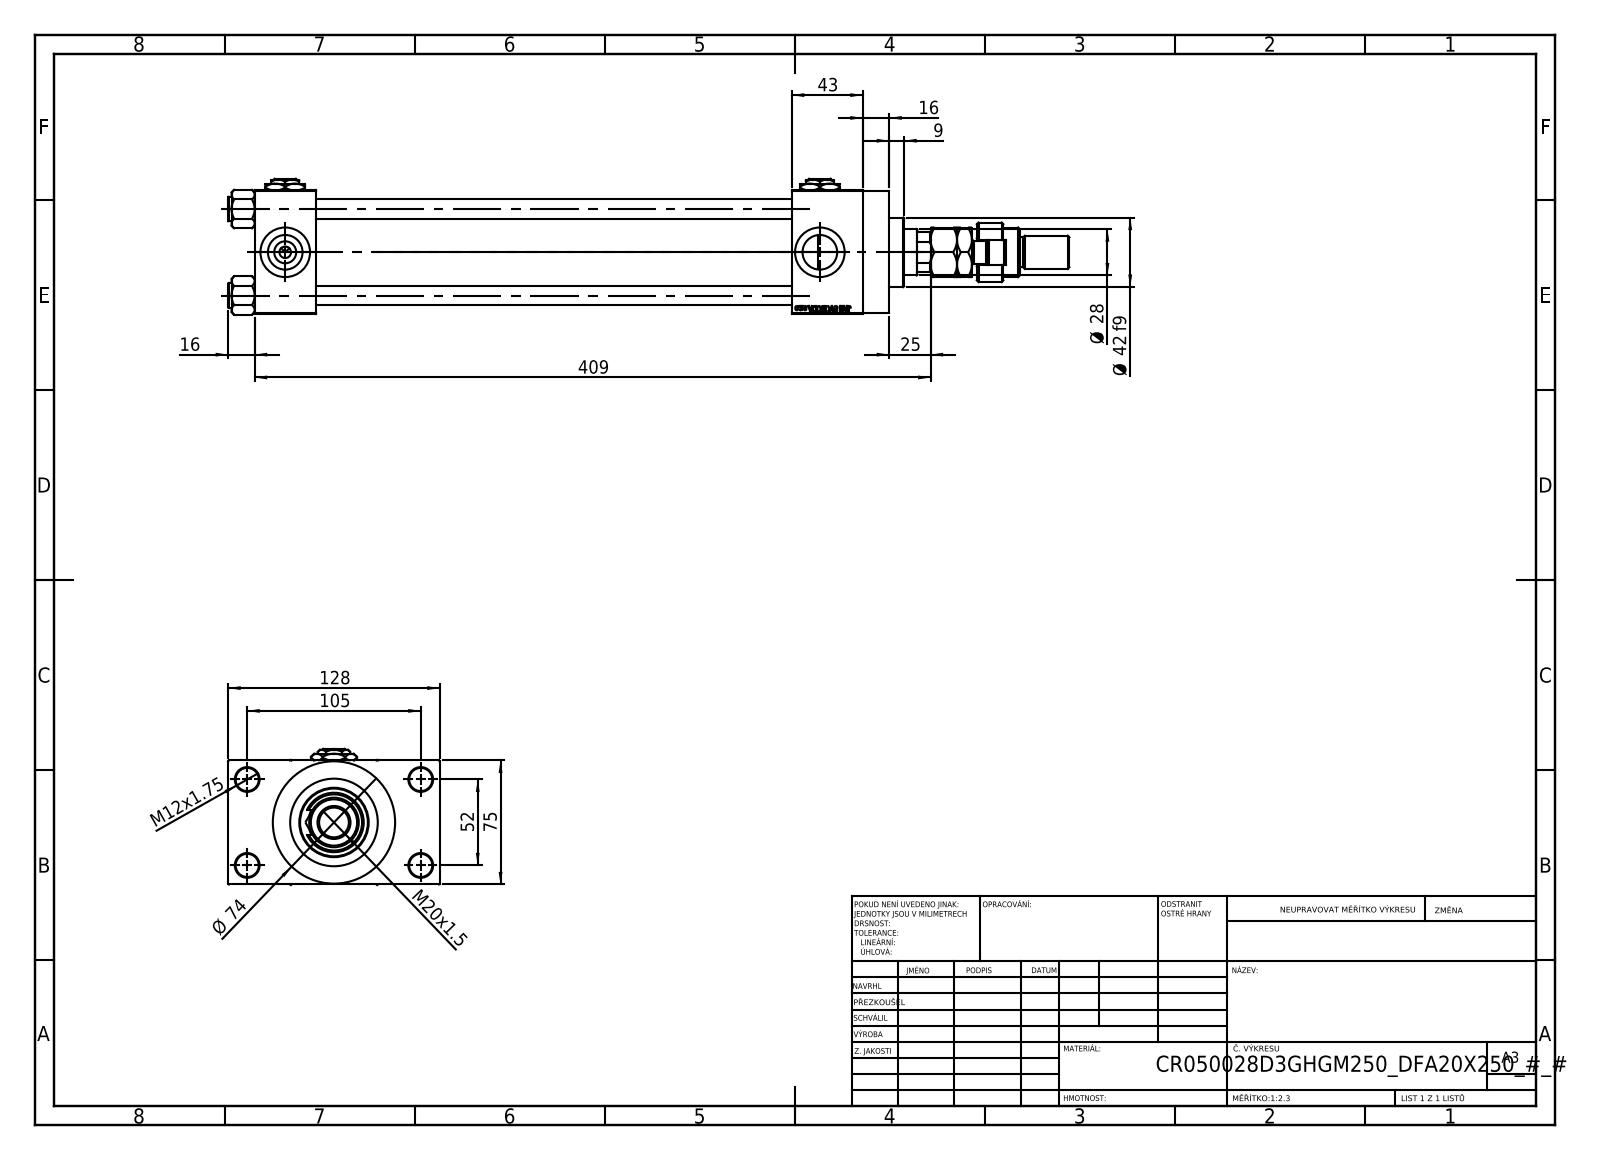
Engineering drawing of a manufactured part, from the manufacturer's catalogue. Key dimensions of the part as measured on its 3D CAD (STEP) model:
Part name (STEP PRODUCT): FEMALE_PART_FOR_DFA; Zatka_pro_OIL_PORT; V215CR_VCP_D; V215CR_D_Body (+4 more)
STEP written by: SolidWorks 2019 (CONFIG_CONTROL_DESIGN)
Units: millimetres
Bodies: 15 solids, 1289 faces (573 planar, 112 cylindrical, 604 other)
Overall size (bounding box): 509 × 128 × 82.27
Volume: 1 211 000 mm³ · Surface area: 319 592 mm²
Round holes (diameter × count): ⌀12 ×4, ⌀14 ×4, ⌀20.96 ×4, ⌀30 ×4, ⌀7 ×3, ⌀18.5 ×1, ⌀28 ×1, ⌀31 ×1, ⌀41 ×1, ⌀50 ×1, ⌀53 ×1
Round bosses / shafts (diameter × count): ⌀15 ×4, ⌀74 ×1, ⌀56 ×1, ⌀42 ×1, ⌀36 ×1, ⌀30 ×1, ⌀22 ×1, ⌀20 ×1
Partial cylindrical surfaces — rounded edges, fillets, slot ends (radius × count): R7.5 ×1, R12 ×1, R13.5 ×1
Main face-to-face distances: 75, 288, 37, 325, 26.5, 43, 368, 331, 101.5, 16
Hole centre spacings: 26.35, 36.98, 52.3, 58.43, 58.59, 78.65, 94.37, 52
